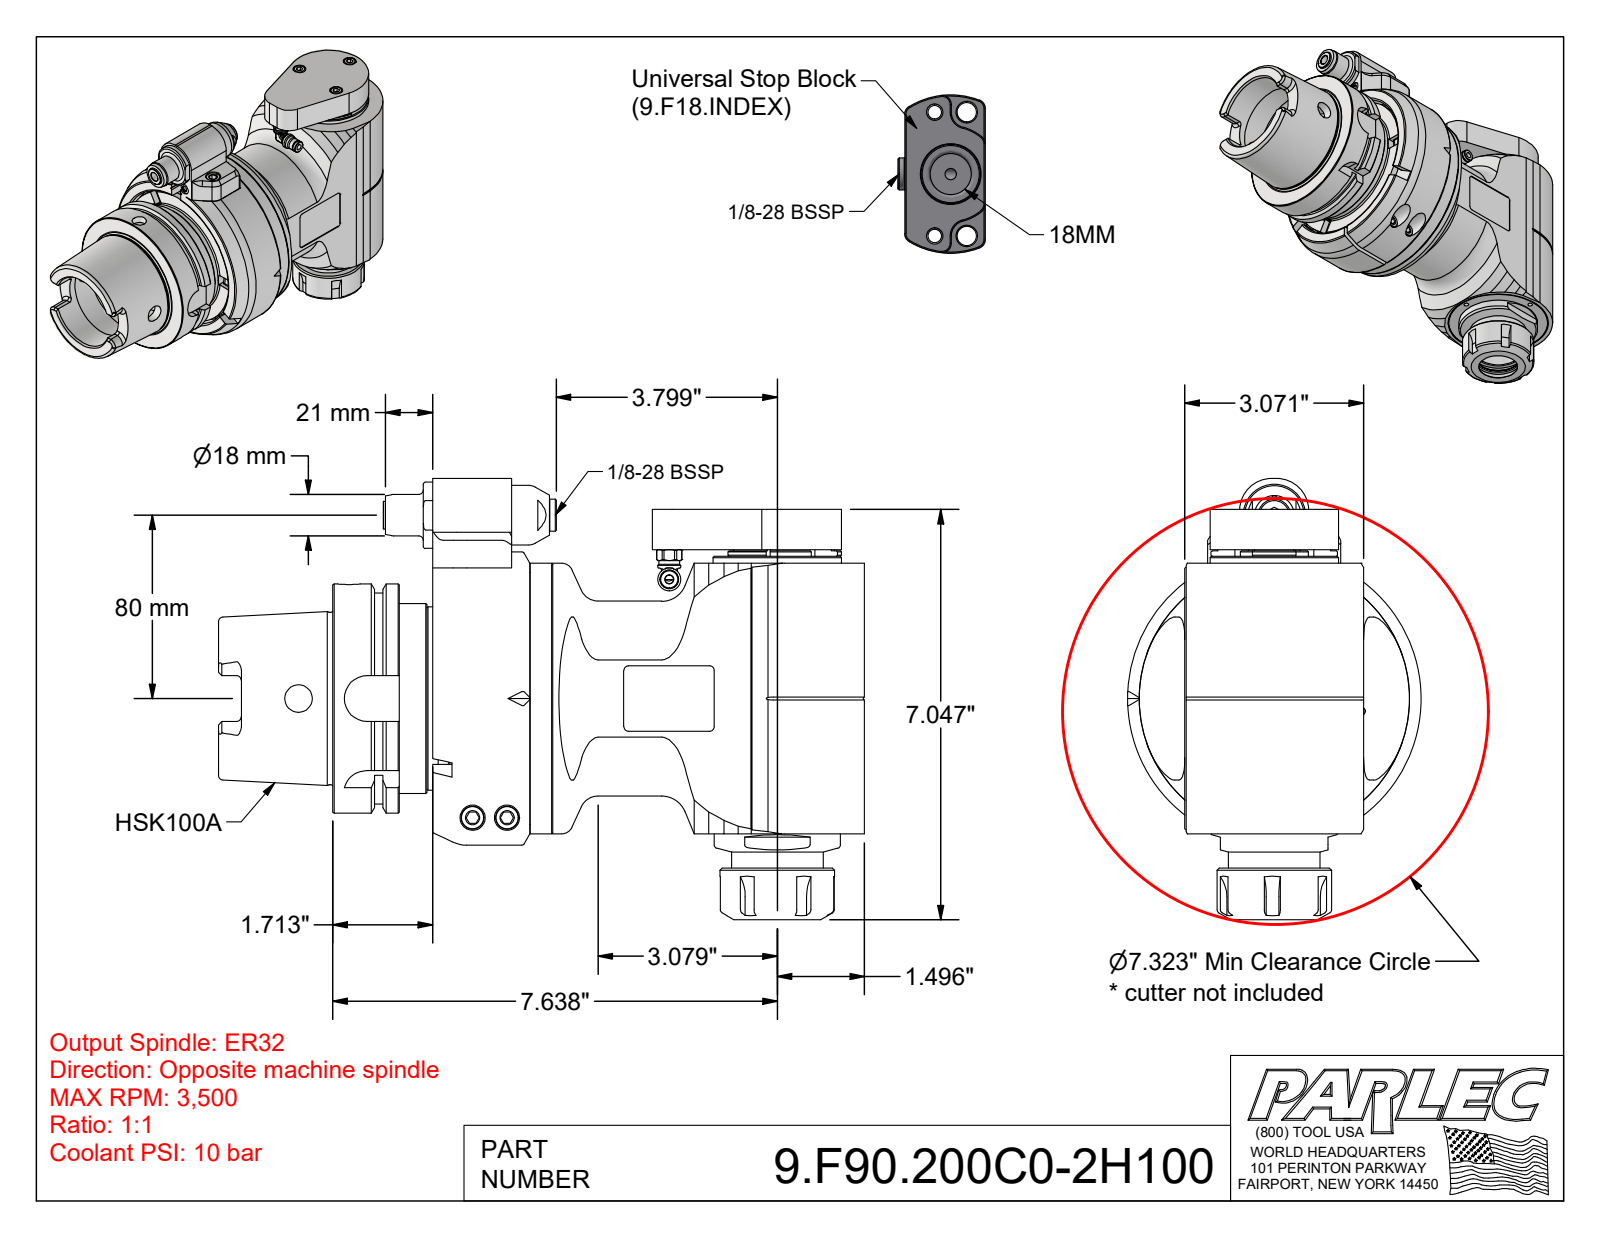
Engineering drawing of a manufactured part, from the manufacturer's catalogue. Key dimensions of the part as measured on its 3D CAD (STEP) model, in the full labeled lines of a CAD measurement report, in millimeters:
Part name (STEP PRODUCT): 9.F90.200C0-2H100; 9_F90_200B0; 9GA21C_518 (Type 2, HSK100 , 80mm)
STEP written by: Autodesk Inventor 2022 (AUTOMOTIVE_DESIGN)
Units: millimetres
Bodies: 7 solids, 924 faces (399 planar, 251 cylindrical, 274 other)
Overall size (bounding box): 282 × 192.5 × 128
Volume: 2 076 000 mm³ · Surface area: 253 900 mm²
Round holes (diameter × count): ⌀10.5 ×20, ⌀3.2 ×4, ⌀5 ×3, ⌀6.5 ×3, ⌀9 ×3, ⌀12.5 ×3, ⌀27 ×3, ⌀2.6 ×2, ⌀3.3 ×2, ⌀3.5 ×2, ⌀4.2 ×2, ⌀8 ×2
Round bosses / shafts (diameter × count): ⌀10 ×5, ⌀12 ×3, ⌀8.5 ×3, ⌀18 ×2, ⌀6 ×2, ⌀2.5 ×2, ⌀128 ×1, ⌀118.1 ×1
Partial cylindrical surfaces — rounded edges, fillets, slot ends (radius × count): R2 ×19, R1 ×18, R3 ×6, R15 ×6, R0.5 ×4, R4 ×4, R4.9 ×4, R10 ×4
Main face-to-face distances: 35, 0.5, 6, 3, 43.5, 17.5, 78, 52, 5, 1
Hole centre spacings: 46.8, 56.3, 66.1, 92.6, 93.5, 45.3, 81.8, 13
